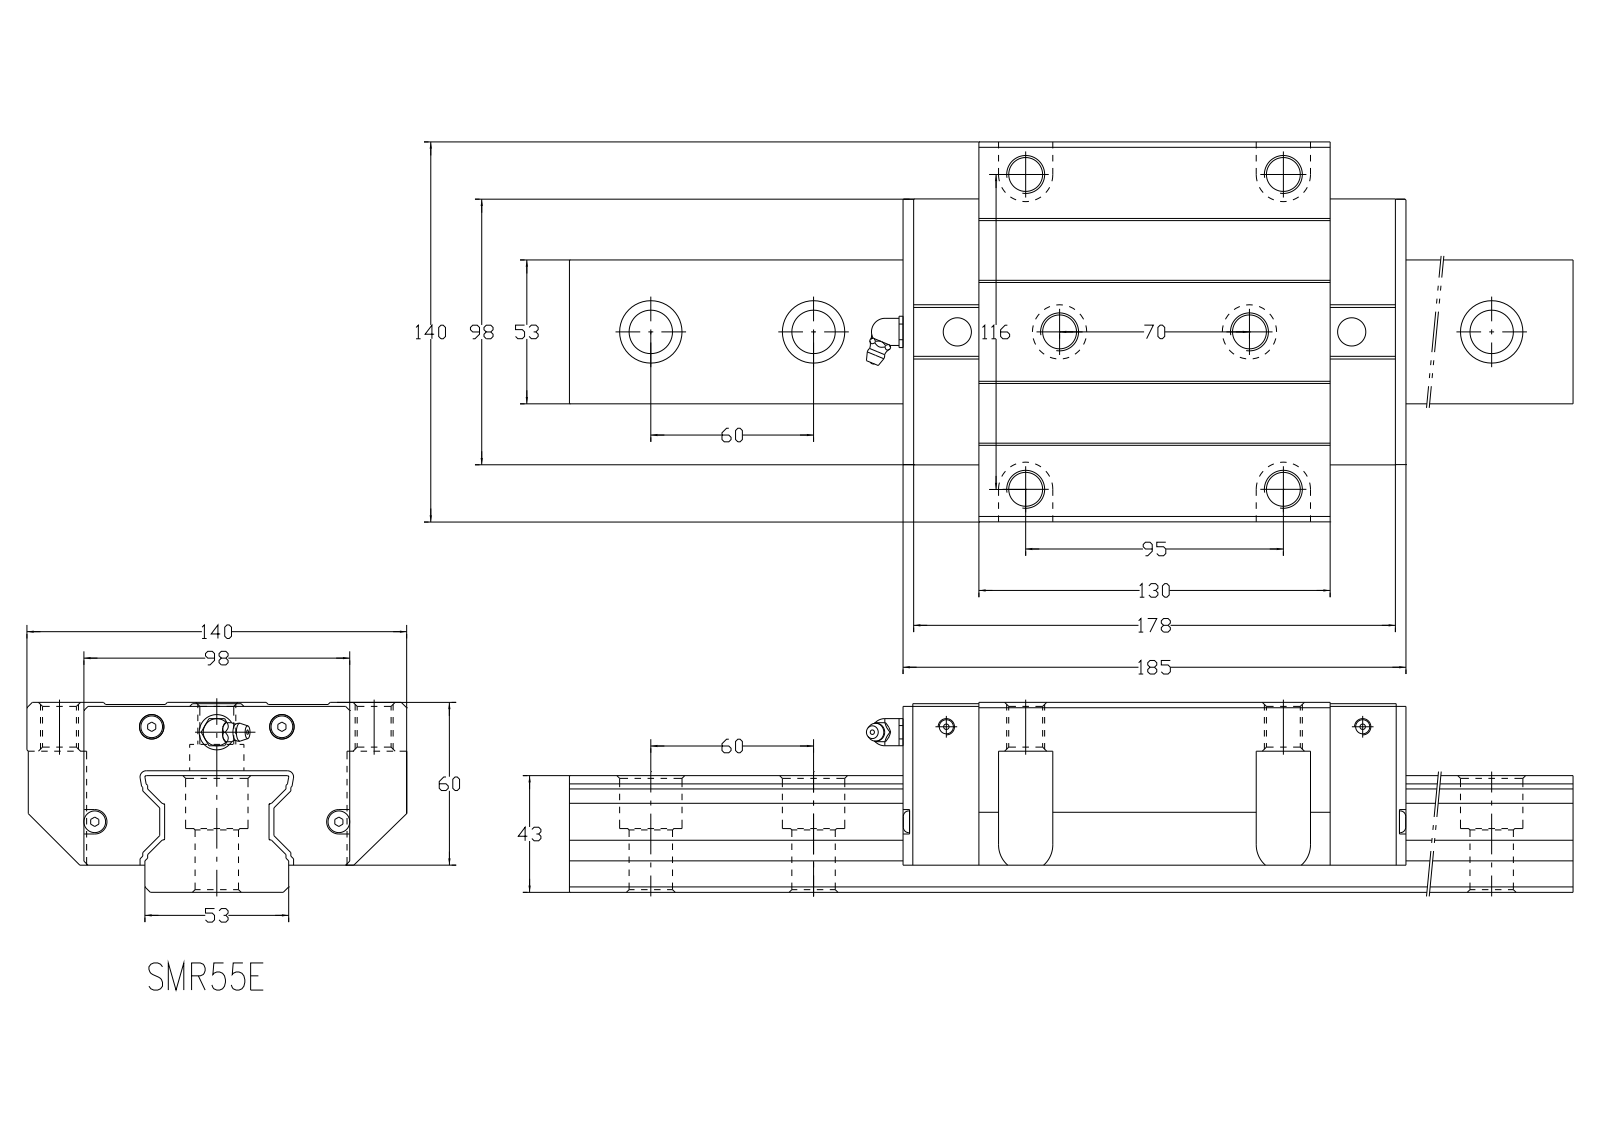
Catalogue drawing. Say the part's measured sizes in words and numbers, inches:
Its 3-D file was written by "Kubotek KeyCreator V6.5.2 (0407) (CONFIG_CONTROL_DESIGN)". It is 3 solids with 260 faces: 153 planar, 90 cylindrical and 17 other. Overall it measures 19.685 by 5.512 by 2.756 inches. Its volume is 116.2 cubic inches and its surface area 351.1 square inches. Round holes: 8 of diameter 0.63, 8 of diameter 0.906, 6 of diameter 0.492, 2 of diameter 0.079, 2 of diameter 0.205, 2 of diameter 0.409, 2 of diameter 0.787, 1 of diameter 0.512. Round bosses or shafts: 1 of diameter 0.394. Partial cylindrical surfaces (rounded edges, fillets, slot ends): 6 of radius 0.02, 4 of radius 0.394. The main face-to-face distances are 1.693, 0.285, 2.756, 1.063, 0.746, 1.801, 0.394, 1.299, 2.362, 1.516. The hole center spacings are 2.362, 4.724, 7.087, 2.336, 2.49, 3.97, 5.254, 9.449.
